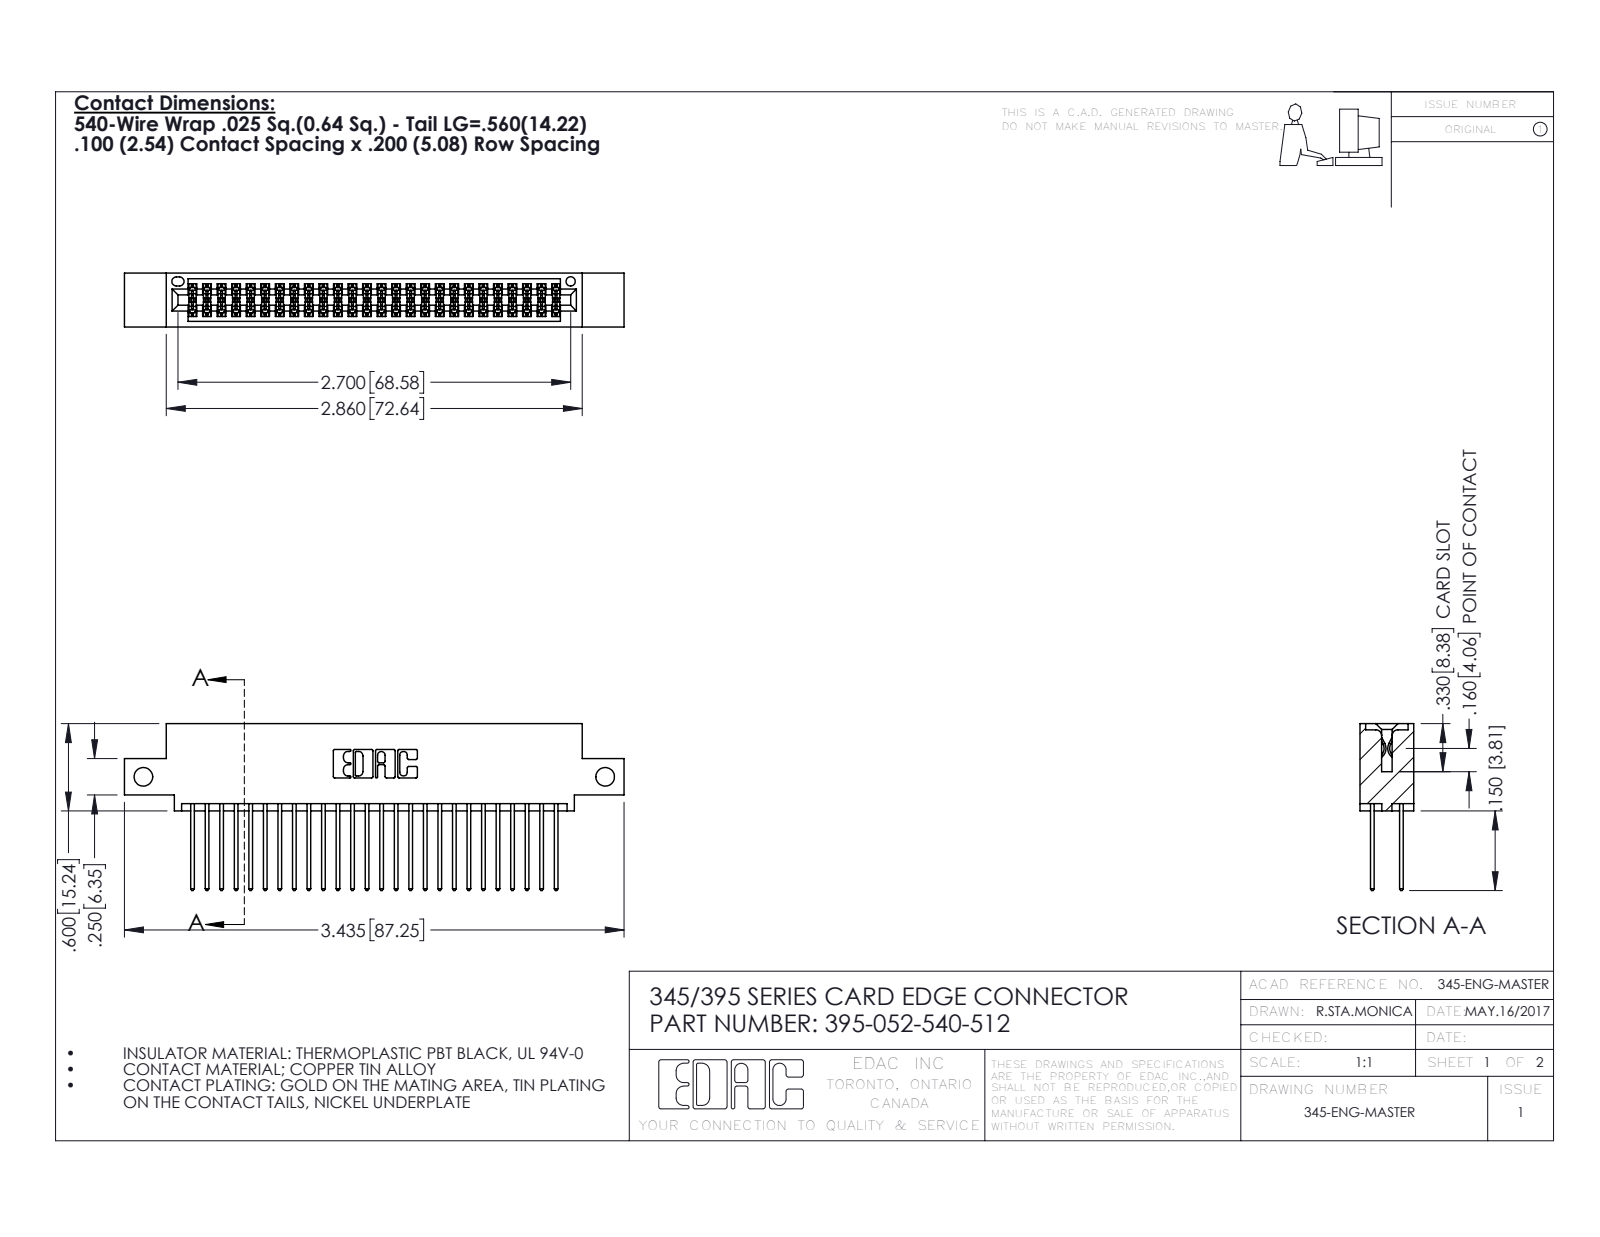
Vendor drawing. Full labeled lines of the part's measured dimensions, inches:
Part name (STEP PRODUCT): 395-052-540-512; 345 Part_0.110 Offset - Side Mount; 345-292-001_345-293-140
STEP written by: SolidWorks 2016 (CONFIG_CONTROL_DESIGN)
Units: inches
Bodies: 53 solids, 2730 faces (1800 planar, 930 cylindrical, 0 other)
Overall size (bounding box): 3.435 × 1.147 × 0.37
Volume: 0.51 in³ · Surface area: 20.03 in²
Round holes (diameter × count): ⌀0.128 ×2, ⌀0.064 ×1
Partial cylindrical surfaces — rounded edges, fillets, slot ends (radius × count): R0.006 ×78, R0.01 ×52, R0.01 ×22, R0.007 ×6, R0.031 ×6, R0.026 ×3, R0.014 ×2, R0.019 ×2
Main face-to-face distances: 0.298, 0.072, 0.2, 0.098, 0.272, 0.025, 0.37, 0.225, 0.175, 0.149
Hole centre spacings: 3.175
